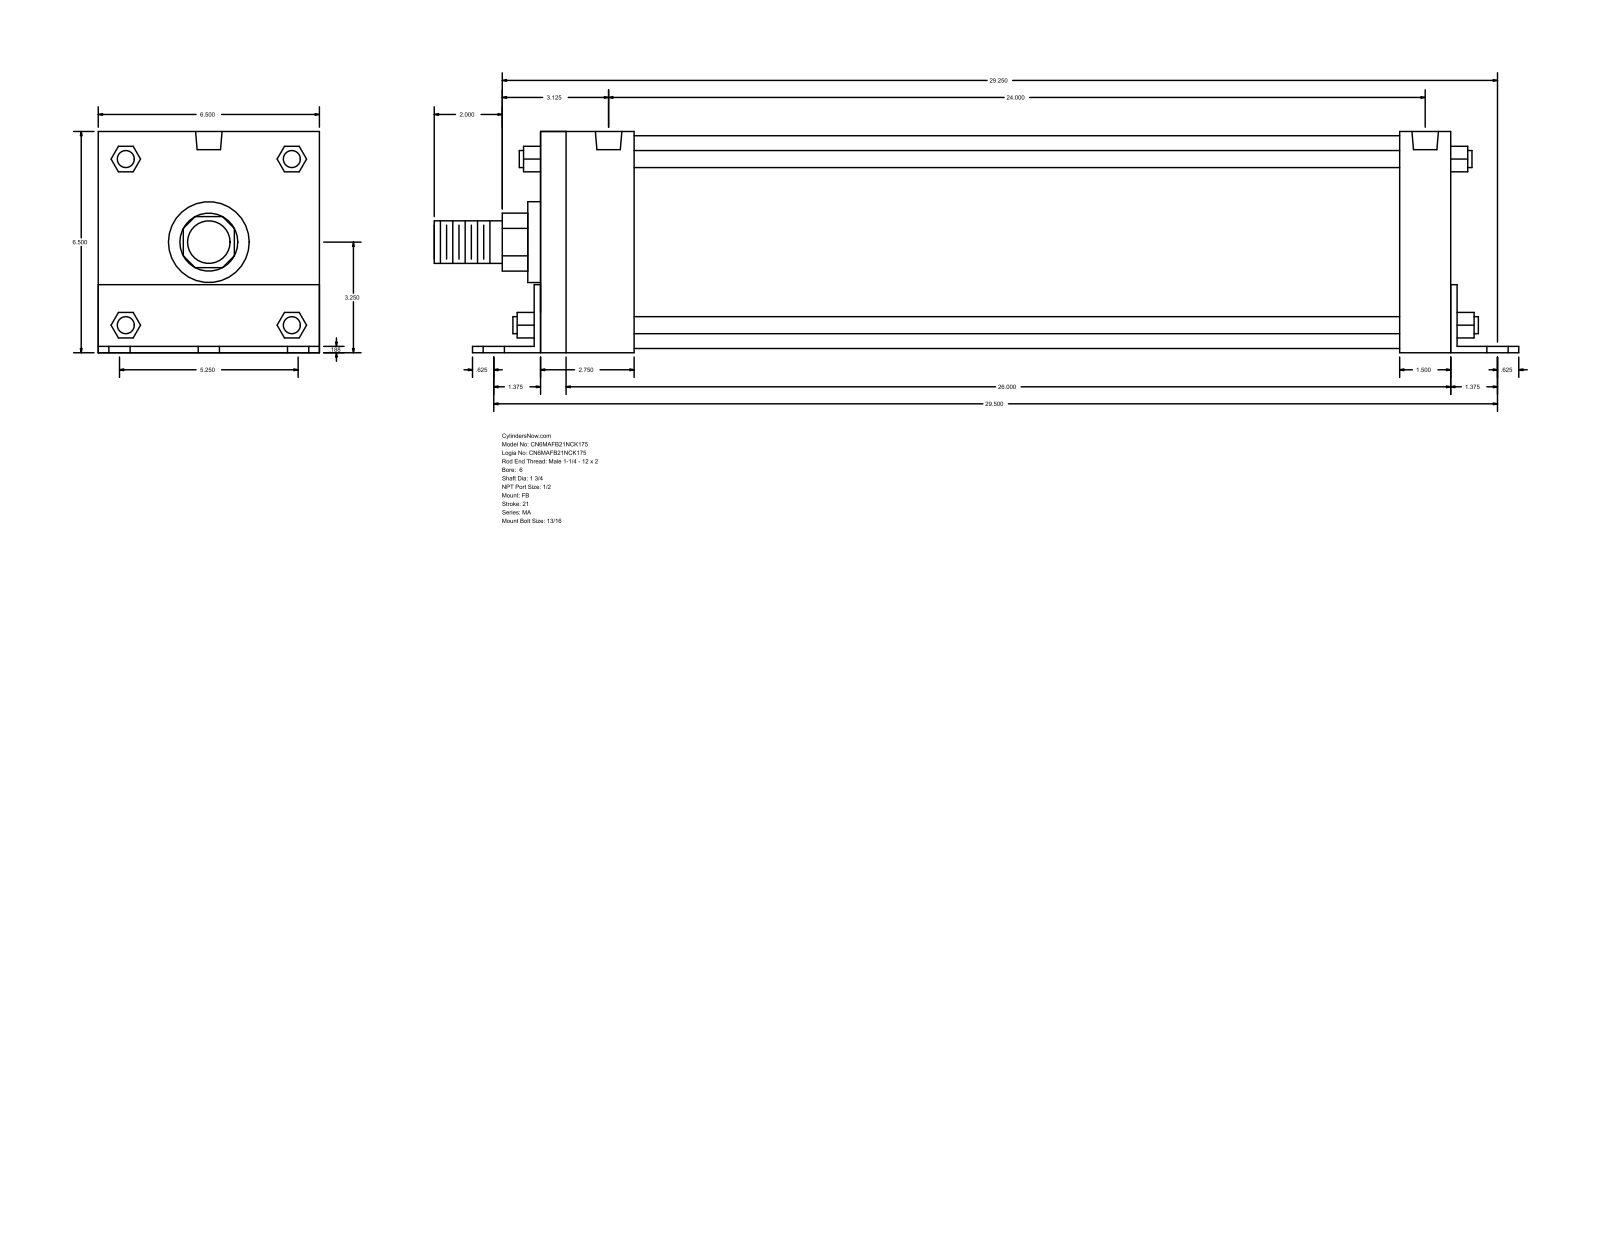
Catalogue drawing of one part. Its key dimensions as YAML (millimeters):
part_name: "MA_FB__0600_1.75"
step_written_by: "GSSL Pune (CONFIG_CONTROL_DESIGN)"
units: millimeters
bodies: {solids: 0, faces: 140, planar: 105, cylindrical: 35, other: 0}
overall_size: [809.62, 165.15, 165.1]
round_holes:
  - {diameter: 20.64, count: 6}
  - {diameter: 17.46, count: 4}
  - {diameter: 19.77, count: 2}
round_bosses_or_shafts:
  - {diameter: 12.7, count: 4}
  - {diameter: 158.75, count: 1}
  - {diameter: 60.33, count: 1}
  - {diameter: 44.45, count: 1}
  - {diameter: 31.75, count: 1}
partial_cylinders:
  - {radius: 21.63, count: 1}
  - {radius: 32.05, count: 1}
face_to_face_distances: [165.1, 4.76, 679.45, 165.15, 4.71, 160.39, 38.1, 69.85, 74.61, 4.77]
hole_center_spacings: [66.67, 752.26, 749.3, 85.78, 108.6, 133.34, 609.6, 666.91]
